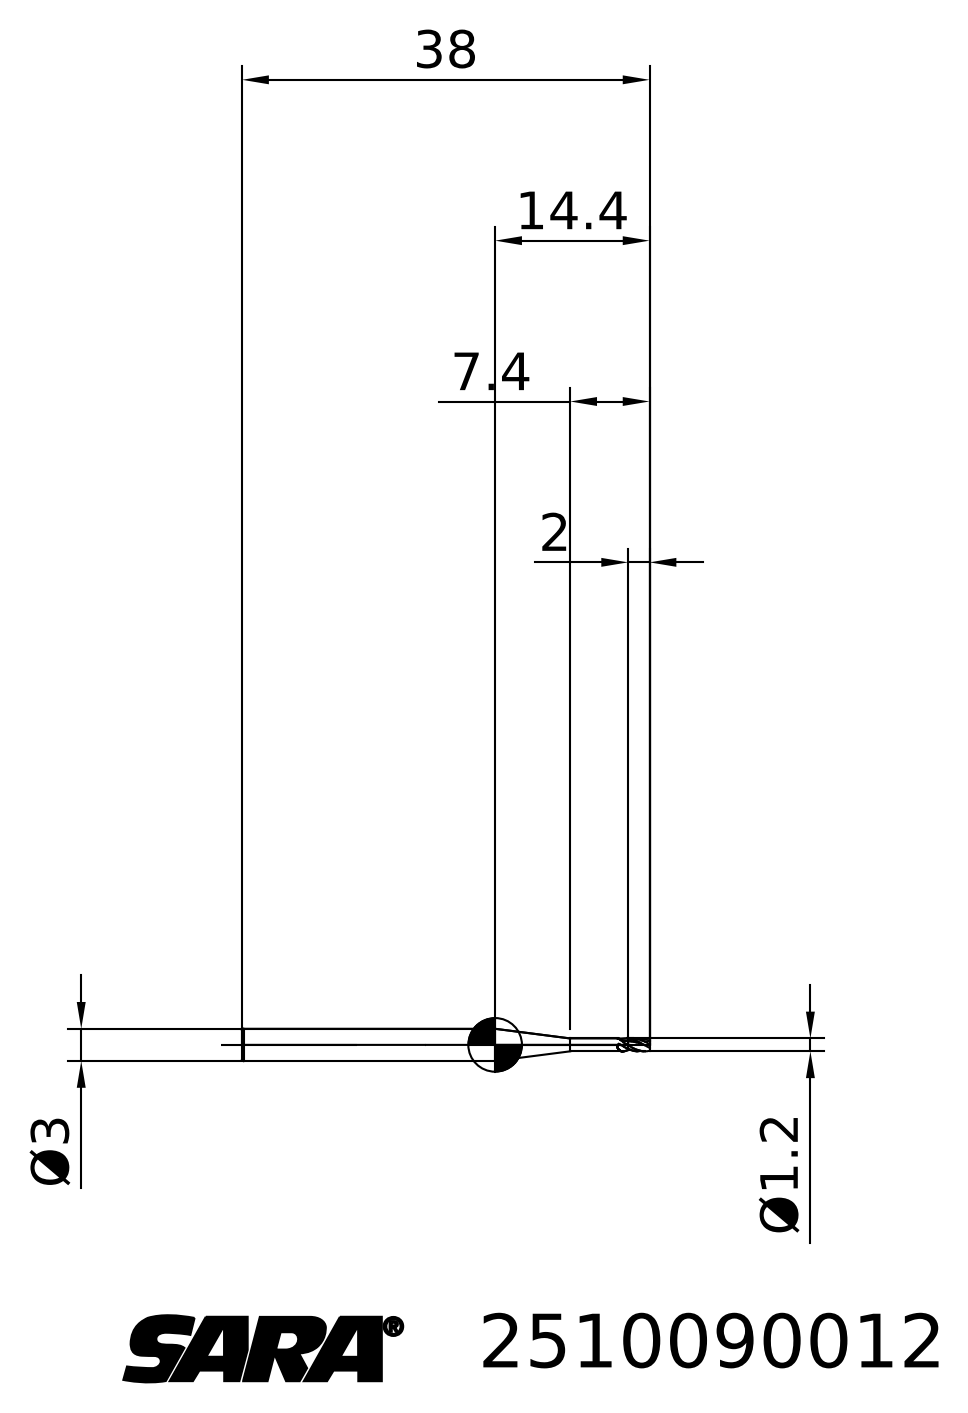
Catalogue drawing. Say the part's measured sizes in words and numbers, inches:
Its 3-D file was written by "TDM (AUTOMOTIVE_DESIGN)". It is 2 solids with 25 faces: 4 planar, 0 cylindrical and 21 other. Overall it measures 1.496 by 0.118 by 0.118 inches. Its volume is 0.012 cubic inches and its surface area 0.474 square inches. The main face-to-face distances are 1.417, 0.079, 1.496.
